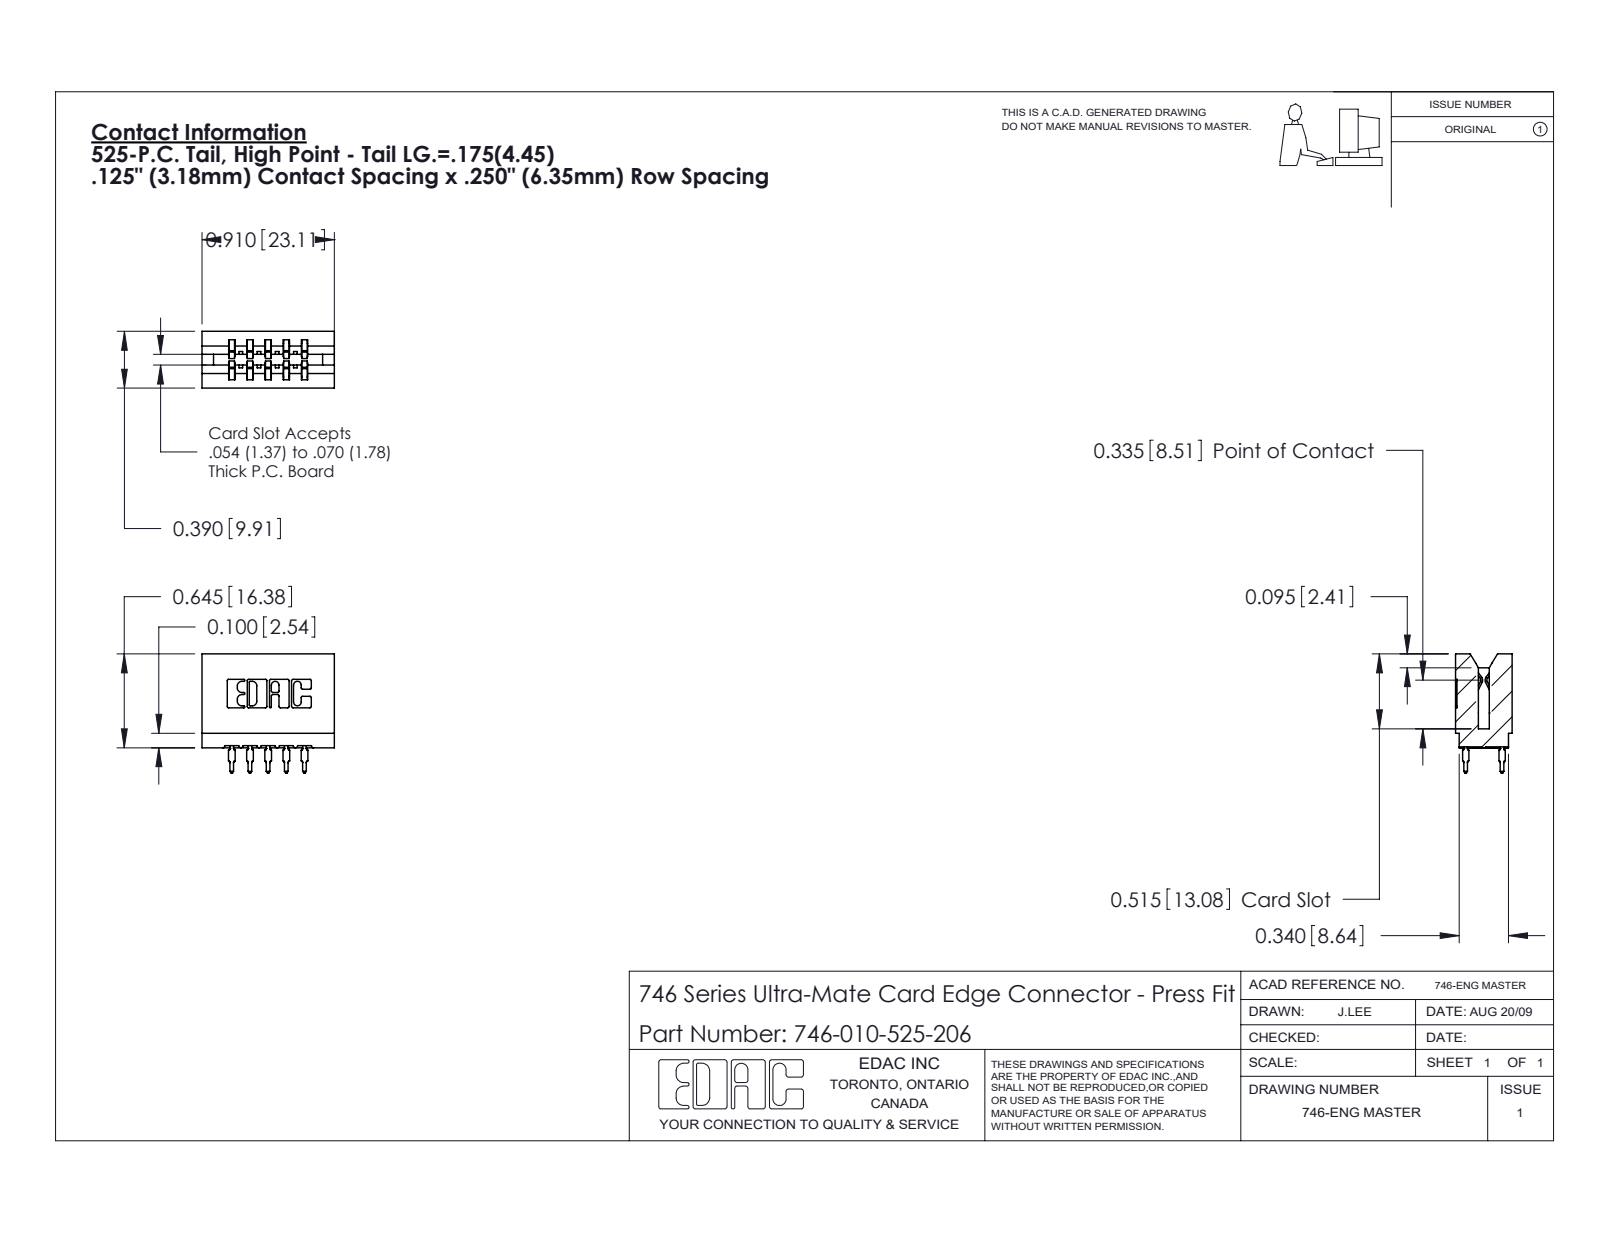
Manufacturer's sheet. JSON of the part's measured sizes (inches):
{"part_name": "746-292-001_525; 746 Part_.515 Slot Depth - 06; 746-010-525-206", "step_written_by": "SolidWorks 2020 (CONFIG_CONTROL_DESIGN)", "units": "inches", "bodies": {"solids": 11, "faces": 993, "planar": 516, "cylindrical": 217, "other": 260}, "overall_size": [0.91, 0.819, 0.39], "volume_in3": 0.164, "surface_area_in2": 5.528, "partial_cylinders_radius": [[0.01, 22], [0.021, 20], [0.005, 8], [0.011, 8], [0.007, 6], [0.015, 6], [0.031, 6], [0.026, 3]], "face_to_face_distances": [0.25, 0.042, 0.057, 0.333, 0.125, 0.125, 0.39, 0.083, 0.208, 0.292]}
